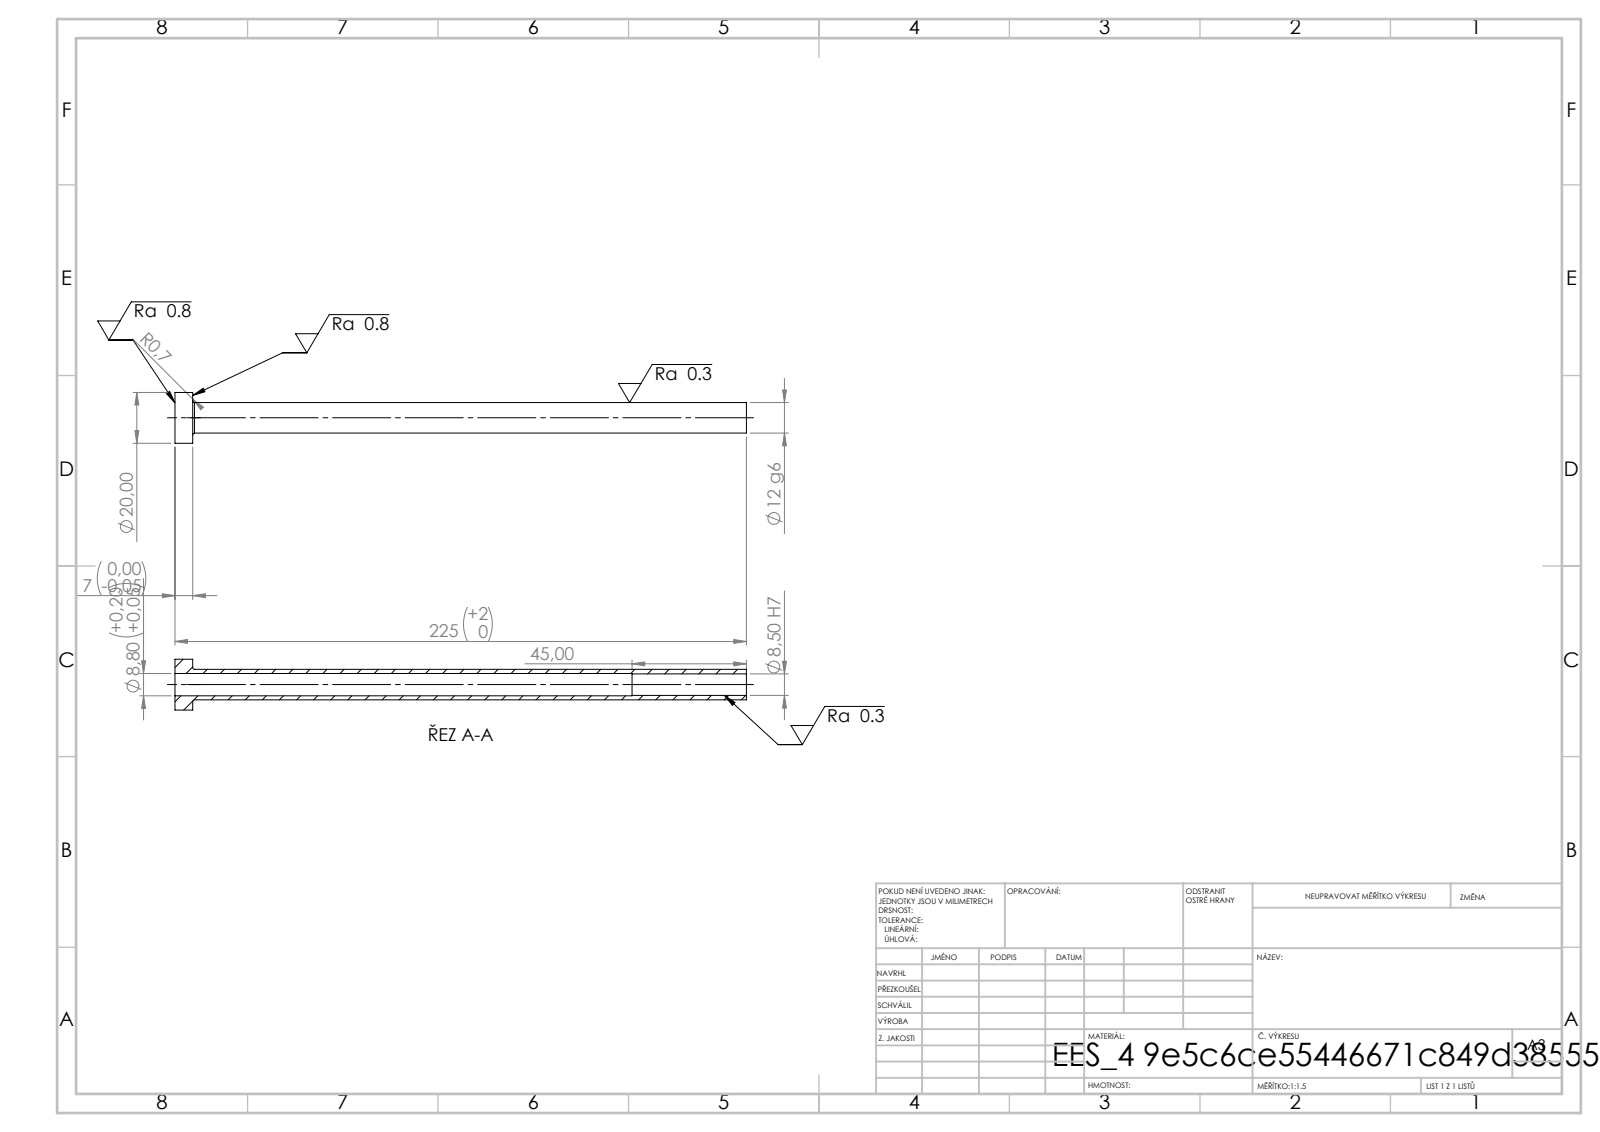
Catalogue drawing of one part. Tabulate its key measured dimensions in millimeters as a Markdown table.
| quantity | value |
| --- | --- |
| STEP written by | SolidWorks 2019 (CONFIG_CONTROL_DESIGN) |
| units | millimeters |
| bodies | 1 solid, 14 faces (4 planar, 8 cylindrical, 2 other) |
| overall size | 225 × 20 × 20 |
| volume | 13 357 mm³ |
| surface area | 15 340 mm² |
| round holes (diameter × count) | 8.5 × 1, 8.8 × 1 |
| round bosses / shafts (diameter × count) | 20 × 1, 12 × 1 |
| main face-to-face distances | 7, 225, 218, 180, 173, 45 |
